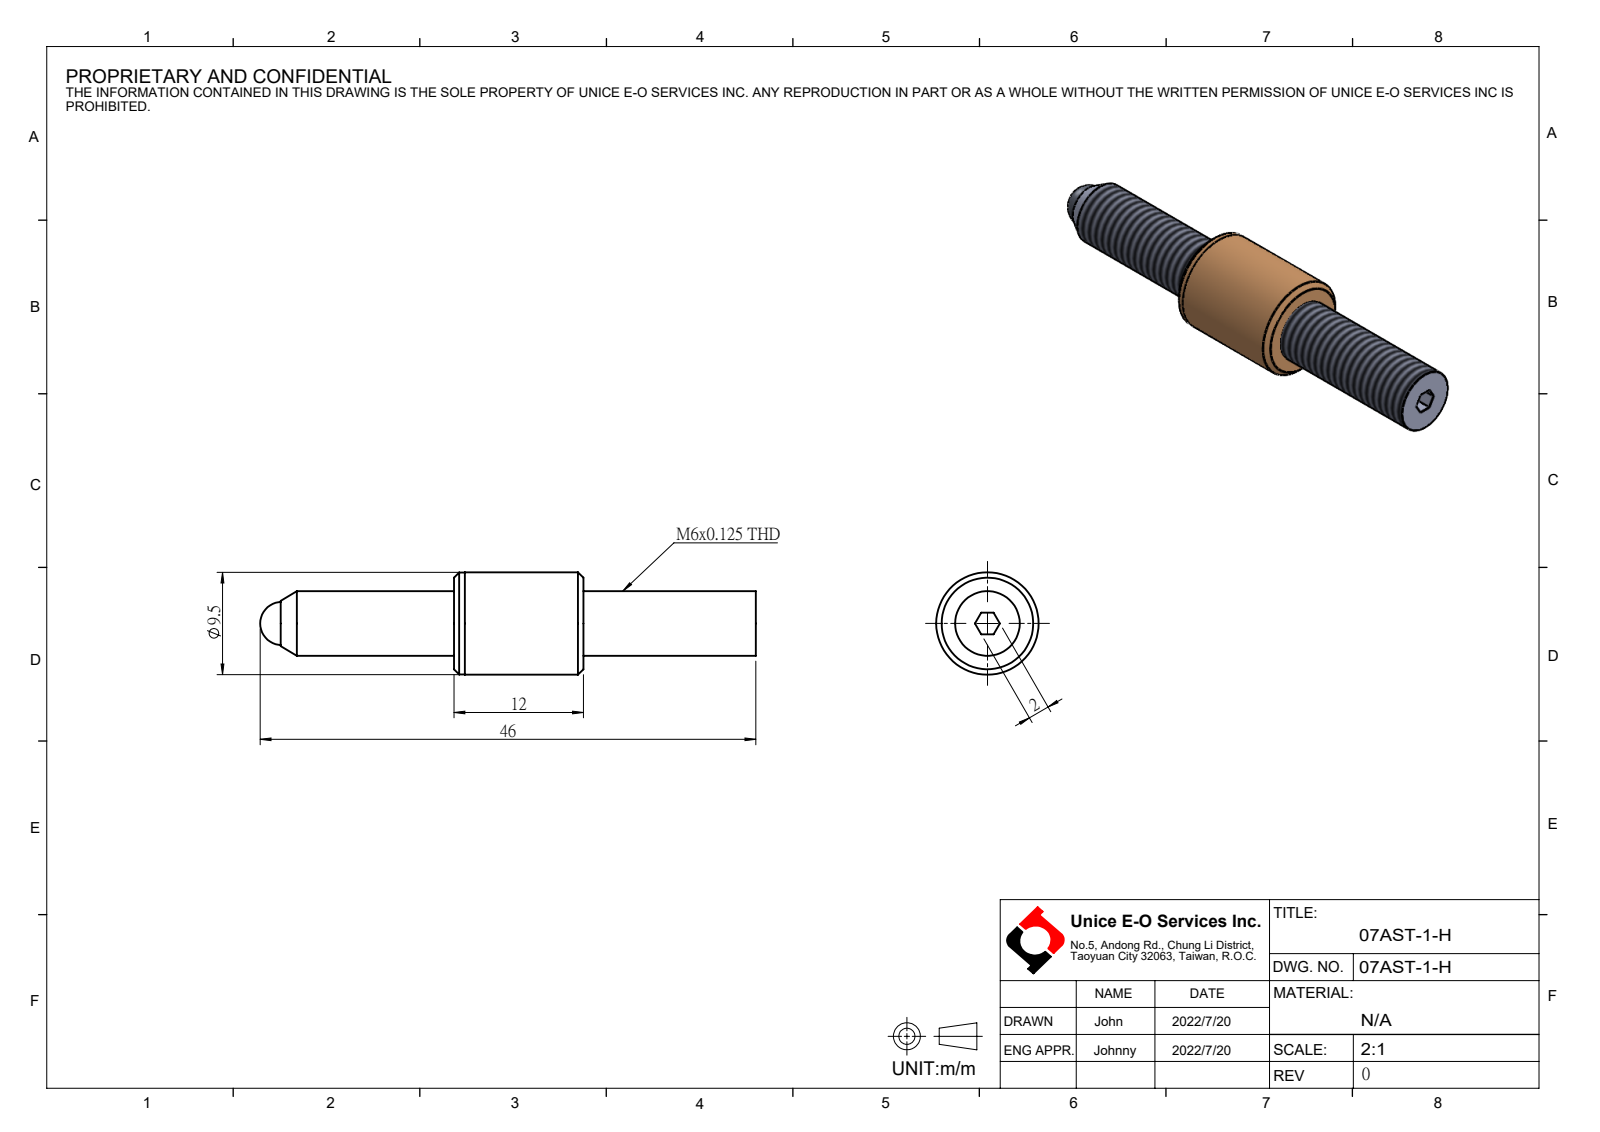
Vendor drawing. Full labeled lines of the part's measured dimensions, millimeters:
Part name (STEP PRODUCT): 07AST-1-H
STEP written by: SolidWorks 2021 (CONFIG_CONTROL_DESIGN)
Units: millimetres
Bodies: 3 solids, 32 faces (12 planar, 10 cylindrical, 10 other)
Overall size (bounding box): 46 × 9.5 × 9.5
Volume: 1 754 mm³ · Surface area: 1 613 mm²
Round holes (diameter × count): ⌀4 ×1, ⌀5.88 ×1
Round bosses / shafts (diameter × count): ⌀9.5 ×1, ⌀9.45 ×1, ⌀6 ×1
Main face-to-face distances: 12, 28, 16, 2, 25, 13, 3, 16.1, 28.1, 41.1
